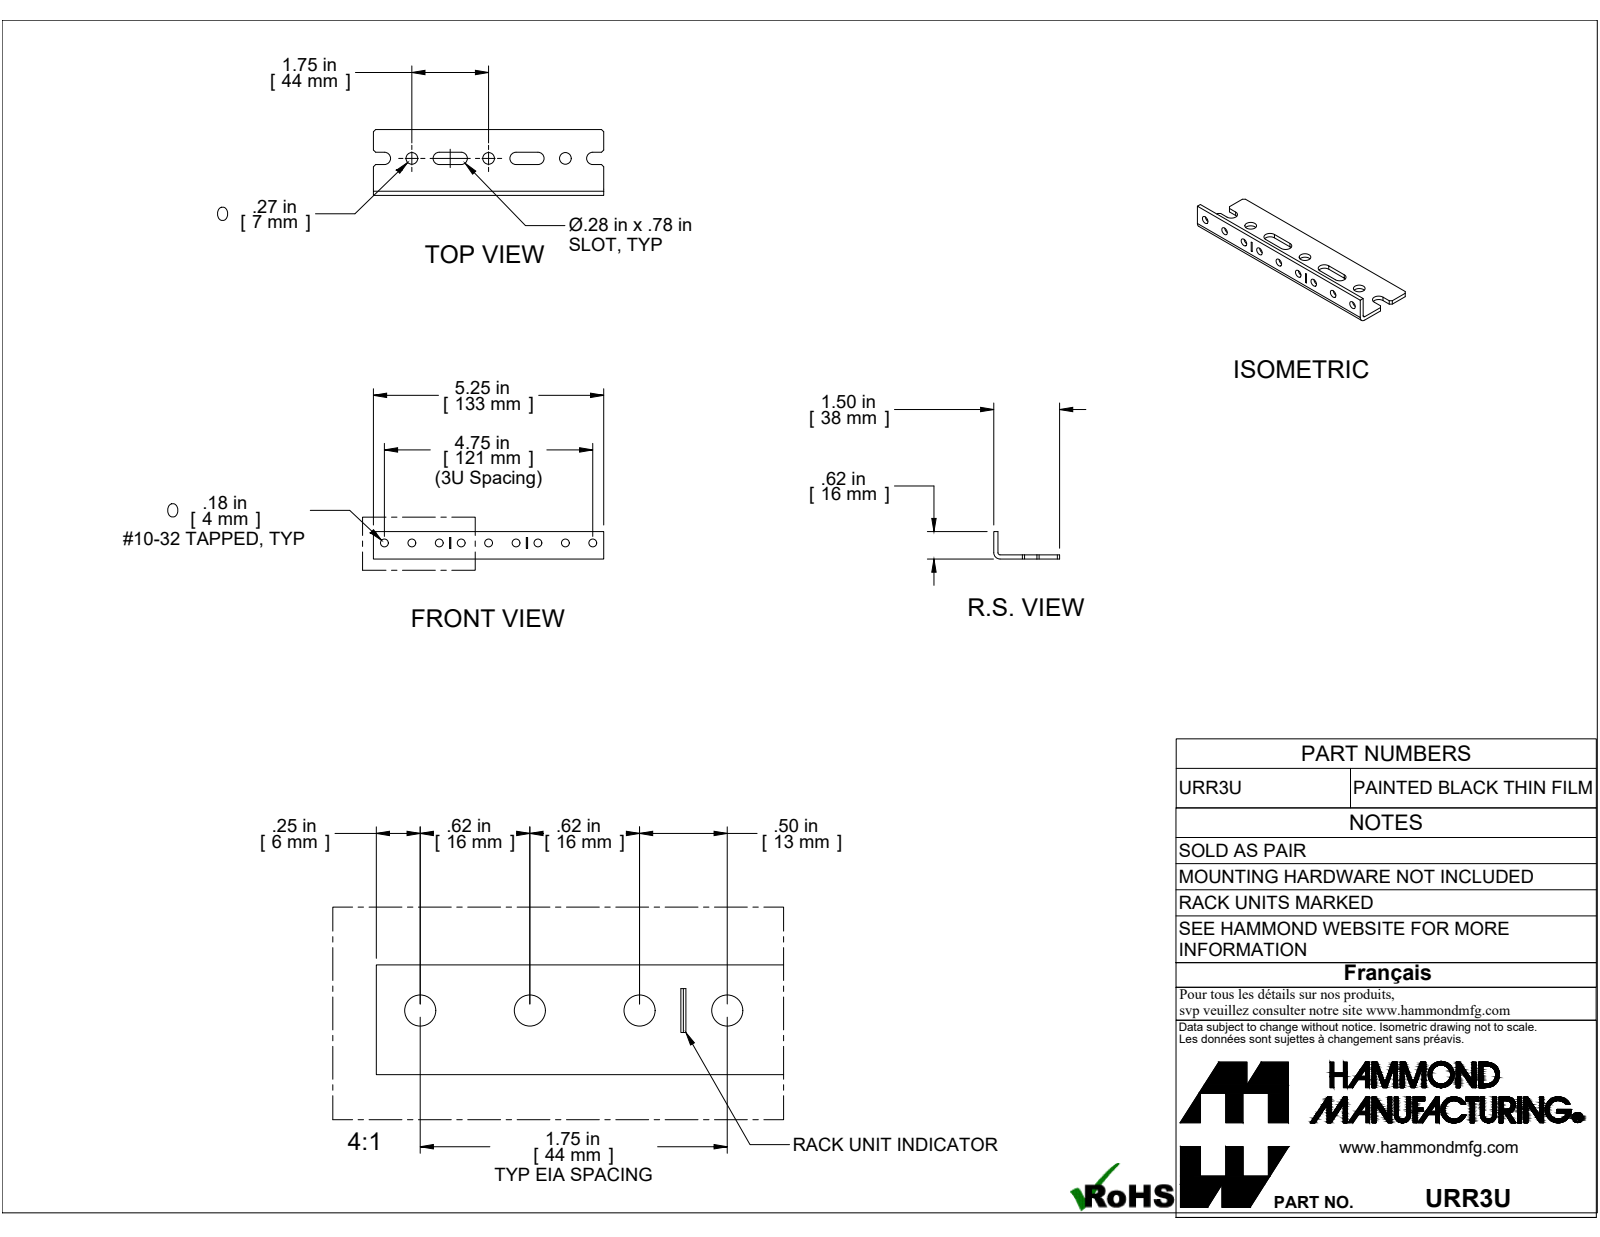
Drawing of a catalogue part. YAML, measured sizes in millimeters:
part_name: "COM57213-3"
step_written_by: "ST-DEVELOPER v16.7 (AUTOMOTIVE_DESIGN)"
units: millimeters
bodies: {solids: 1, faces: 52, planar: 32, cylindrical: 20, other: 0}
overall_size: [133.35, 38.1, 15.88]
volume: 14692
surface_area: 13838
round_holes:
  - {diameter: 4.5, count: 9}
  - {diameter: 6.76, count: 3}
partial_cylinders:
  - {radius: 3.57, count: 6}
  - {radius: 1.22, count: 1}
  - {radius: 3.63, count: 1}
face_to_face_distances: [2.41, 15.88, 13.47, 38.1, 35.69, 133.34, 17.84, 24.98, 15.43, 22.57]
hole_center_spacings: [44.45, 15.88, 28.57, 60.33, 88.9, 31.76, 12.69, 73.02]
